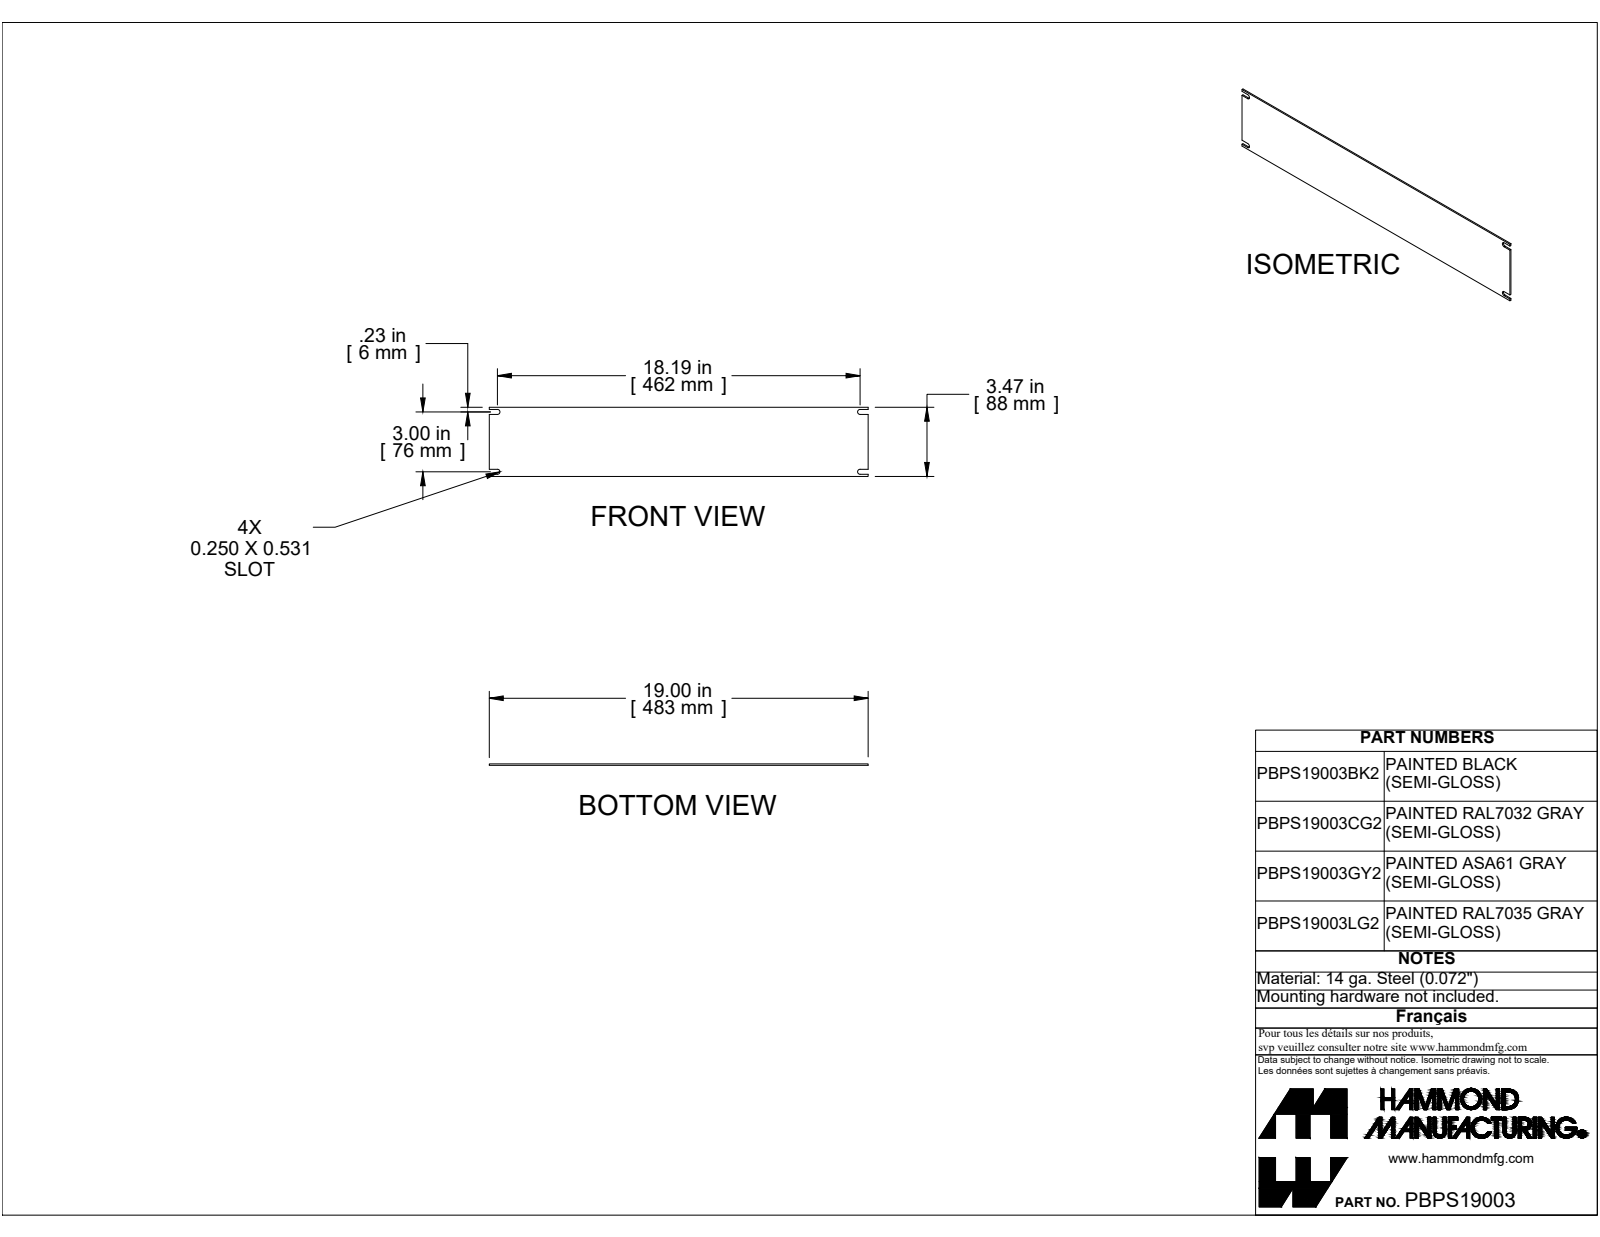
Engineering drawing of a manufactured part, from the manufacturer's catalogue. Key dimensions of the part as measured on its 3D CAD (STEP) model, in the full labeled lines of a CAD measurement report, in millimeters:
Part name (STEP PRODUCT): PBPS19003GY2
STEP written by: SolidWorks 2019 (CONFIG_CONTROL_DESIGN)
Units: millimetres
Bodies: 1 solid, 22 faces (18 planar, 4 cylindrical, 0 other)
Overall size (bounding box): 482.6 × 88.1 × 1.8
Volume: 77 150 mm³ · Surface area: 86 640 mm²
Partial cylindrical surfaces — rounded edges, fillets, slot ends (radius × count): R3.2 ×4
Main face-to-face distances: 1.8, 88.1, 482.6, 9.1, 79, 2.8, 85.3, 6.4, 76.2, 6.4
